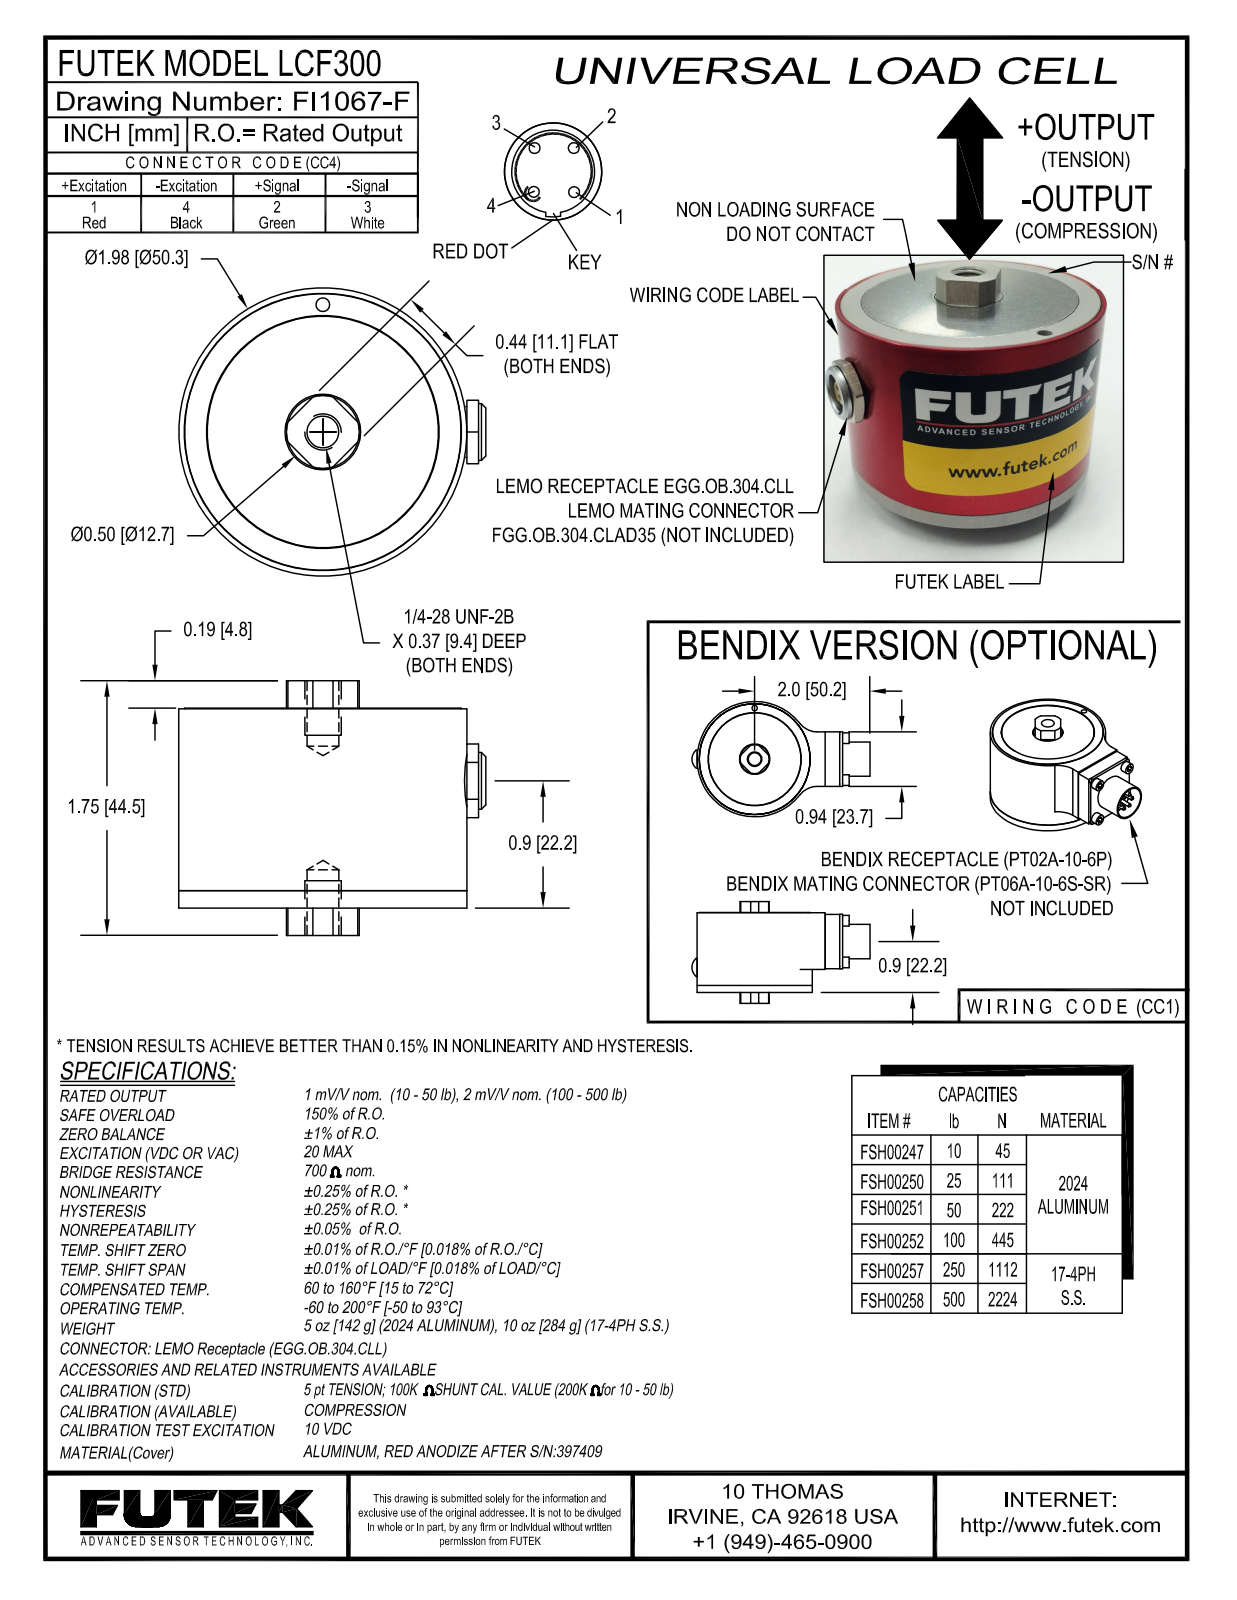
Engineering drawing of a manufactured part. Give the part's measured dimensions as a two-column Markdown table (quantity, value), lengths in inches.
| quantity | value |
| --- | --- |
| part name | LCF300 Bendix; ~~~~PART1; 6PIN-BENDIX; SHC4-40 (+1 more) |
| STEP written by | Autodesk Inventor 2008 (AUTOMOTIVE_DESIGN) |
| units | inches |
| bodies | 7 solids, 180 faces (103 planar, 60 cylindrical, 17 other) |
| overall size | 2.597 × 2.597 × 1.75 |
| volume | 4.373 in³ |
| surface area | 48.78 in² |
| round holes (diameter × count) | 0.089 × 4, 0.12 × 4, 0.13 × 4, 0.6 × 2, 0.094 × 1, 0.219 × 1, 0.52 × 1, 0.55 × 1, 1.5 × 1, 1.6 × 1, 1.905 × 1 |
| round bosses / shafts (diameter × count) | 0.06 × 12, 0.183 × 4, 0.112 × 4, 1.98 × 1, 1.9 × 1, 1.59 × 1, 0.59 × 1, 0.573 × 1 |
| partial cylindrical surfaces (radius × count) | 0.05 × 4, 0.375 × 2 |
| main face-to-face distances | 0.115, 1.19, 0.035, 0.15, 1.225, 1.34, 1.365, 0.03, 1.22, 1.335 |
| hole center spacings | 0.719, 0.508, 0.719, 0.72, 0.509, 0.509, 0.509, 0.72 |
